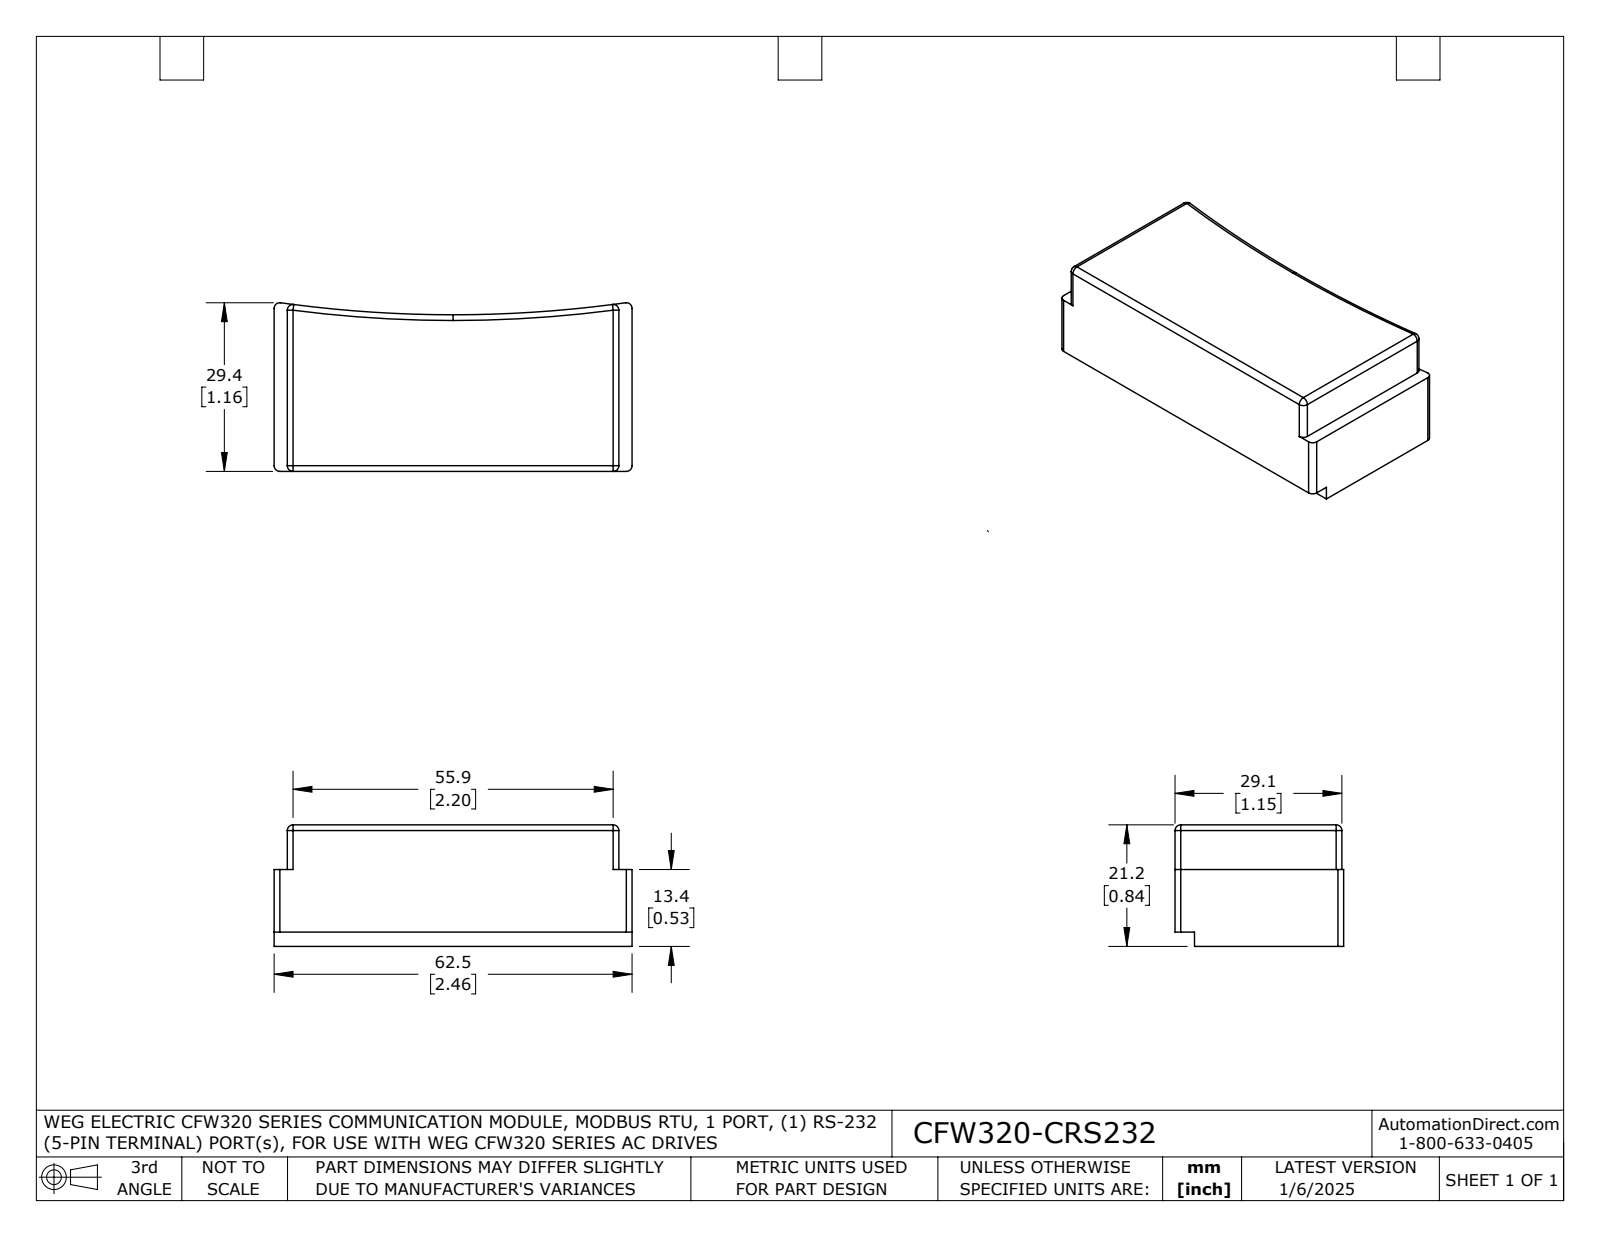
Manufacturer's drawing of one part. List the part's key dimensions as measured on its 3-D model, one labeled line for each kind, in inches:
Part name (STEP PRODUCT): CFW320-CRS232
STEP written by: SolidWorks 2021 (AUTOMOTIVE_DESIGN)
Units: inches
Bodies: 1 solid, 33 faces (11 planar, 16 cylindrical, 6 other)
Overall size (bounding box): 2.461 × 1.159 × 0.835
Volume: 2.173 in³ · Surface area: 11.18 in²
Partial cylindrical surfaces — rounded edges, fillets, slot ends (radius × count): R0.039 ×11, R8.543 ×1
Main face-to-face distances: 0.835, 0.091, 2.37, 2.461, 0.098, 0.737, 2.28, 0.134, 0.528, 0.43
